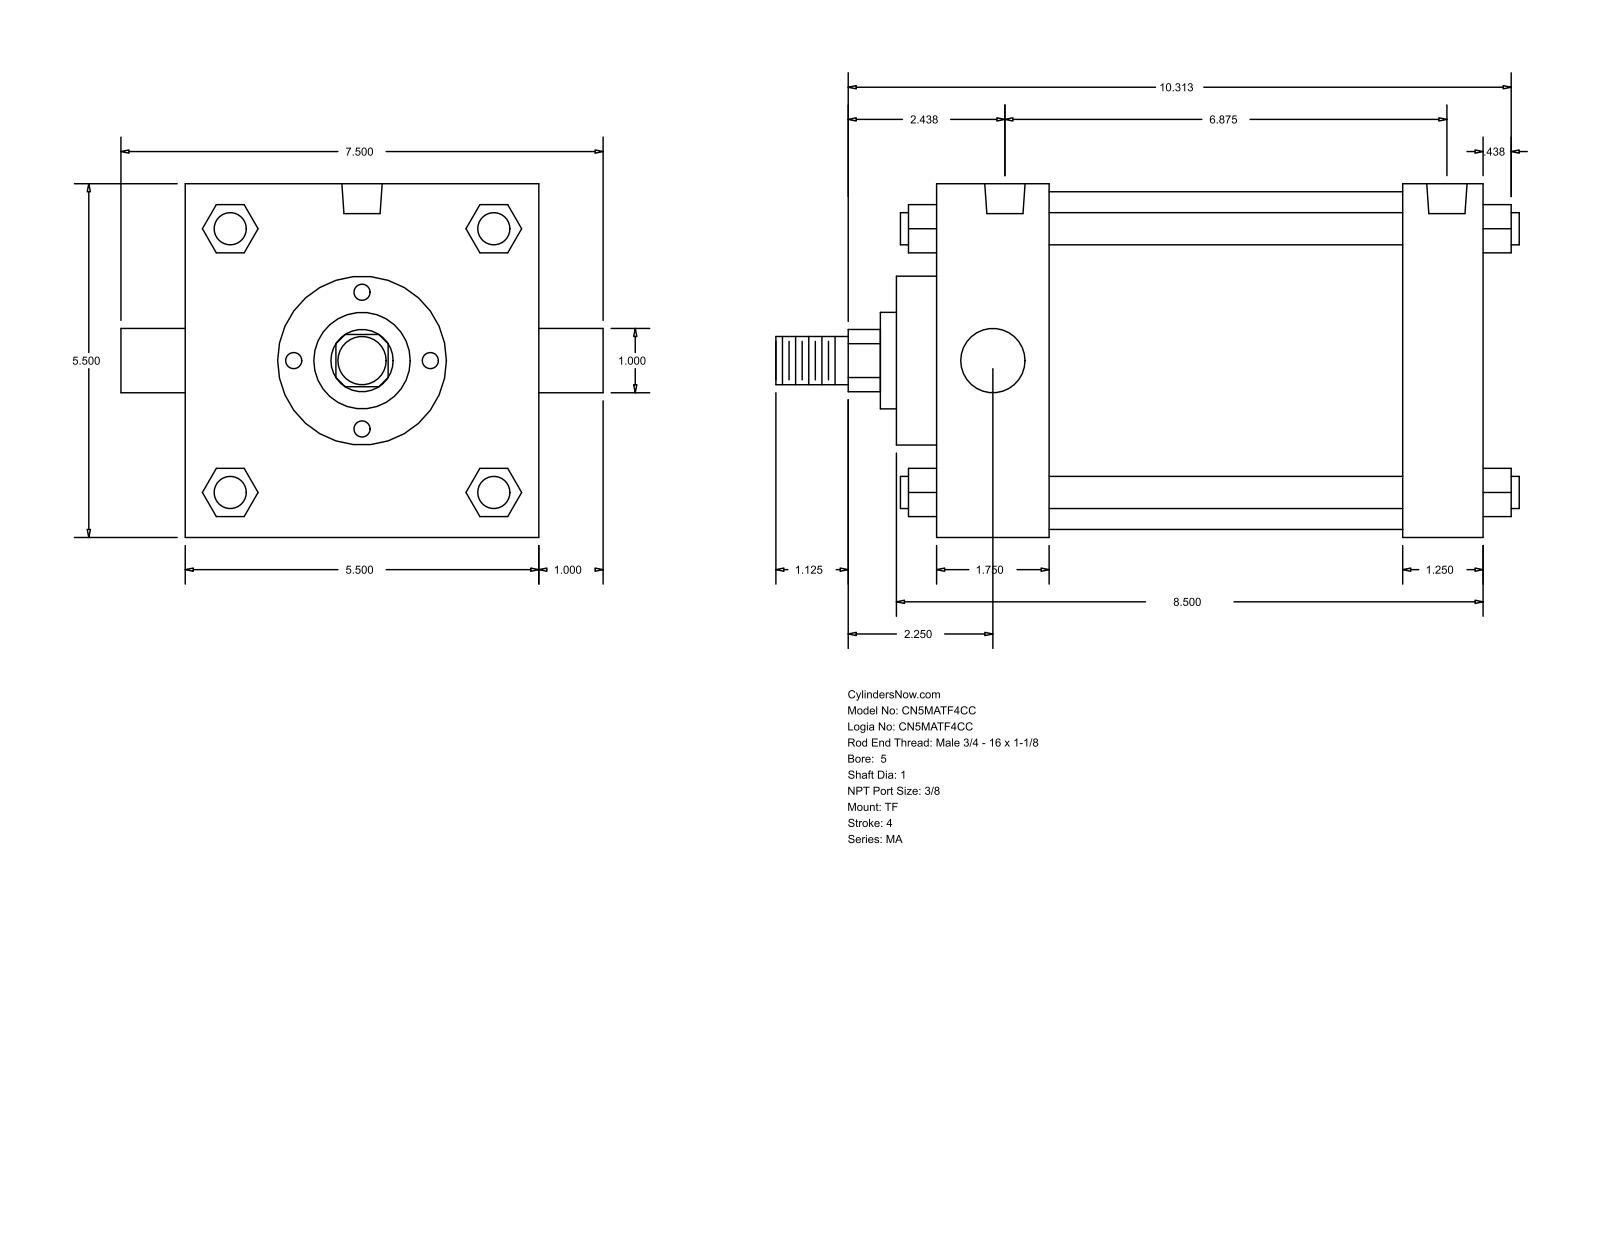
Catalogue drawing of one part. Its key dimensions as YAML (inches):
part_name: "MA_TF__0500_1"
step_written_by: "GSSL Pune (CONFIG_CONTROL_DESIGN)"
units: inches
bodies: {solids: 0, faces: 122, planar: 93, cylindrical: 29, other: 0}
overall_size: [11.563, 7.5, 5.5]
round_holes:
  - {diameter: 0.437, count: 3}
  - {diameter: 0.627, count: 2}
round_bosses_or_shafts:
  - {diameter: 0.5, count: 4}
  - {diameter: 1, count: 2}
  - {diameter: 5.25, count: 1}
  - {diameter: 2.625, count: 1}
  - {diameter: 1.5, count: 1}
  - {diameter: 0.75, count: 1}
partial_cylinders:
  - {radius: 0.484, count: 1}
face_to_face_distances: [5.5, 8.5, 7.25, 1.25, 1.75, 5.5, 6.75, 0.625, 2.375, 7.875]
hole_center_spacings: [0.187, 6.688, 6.5, 6.875]
